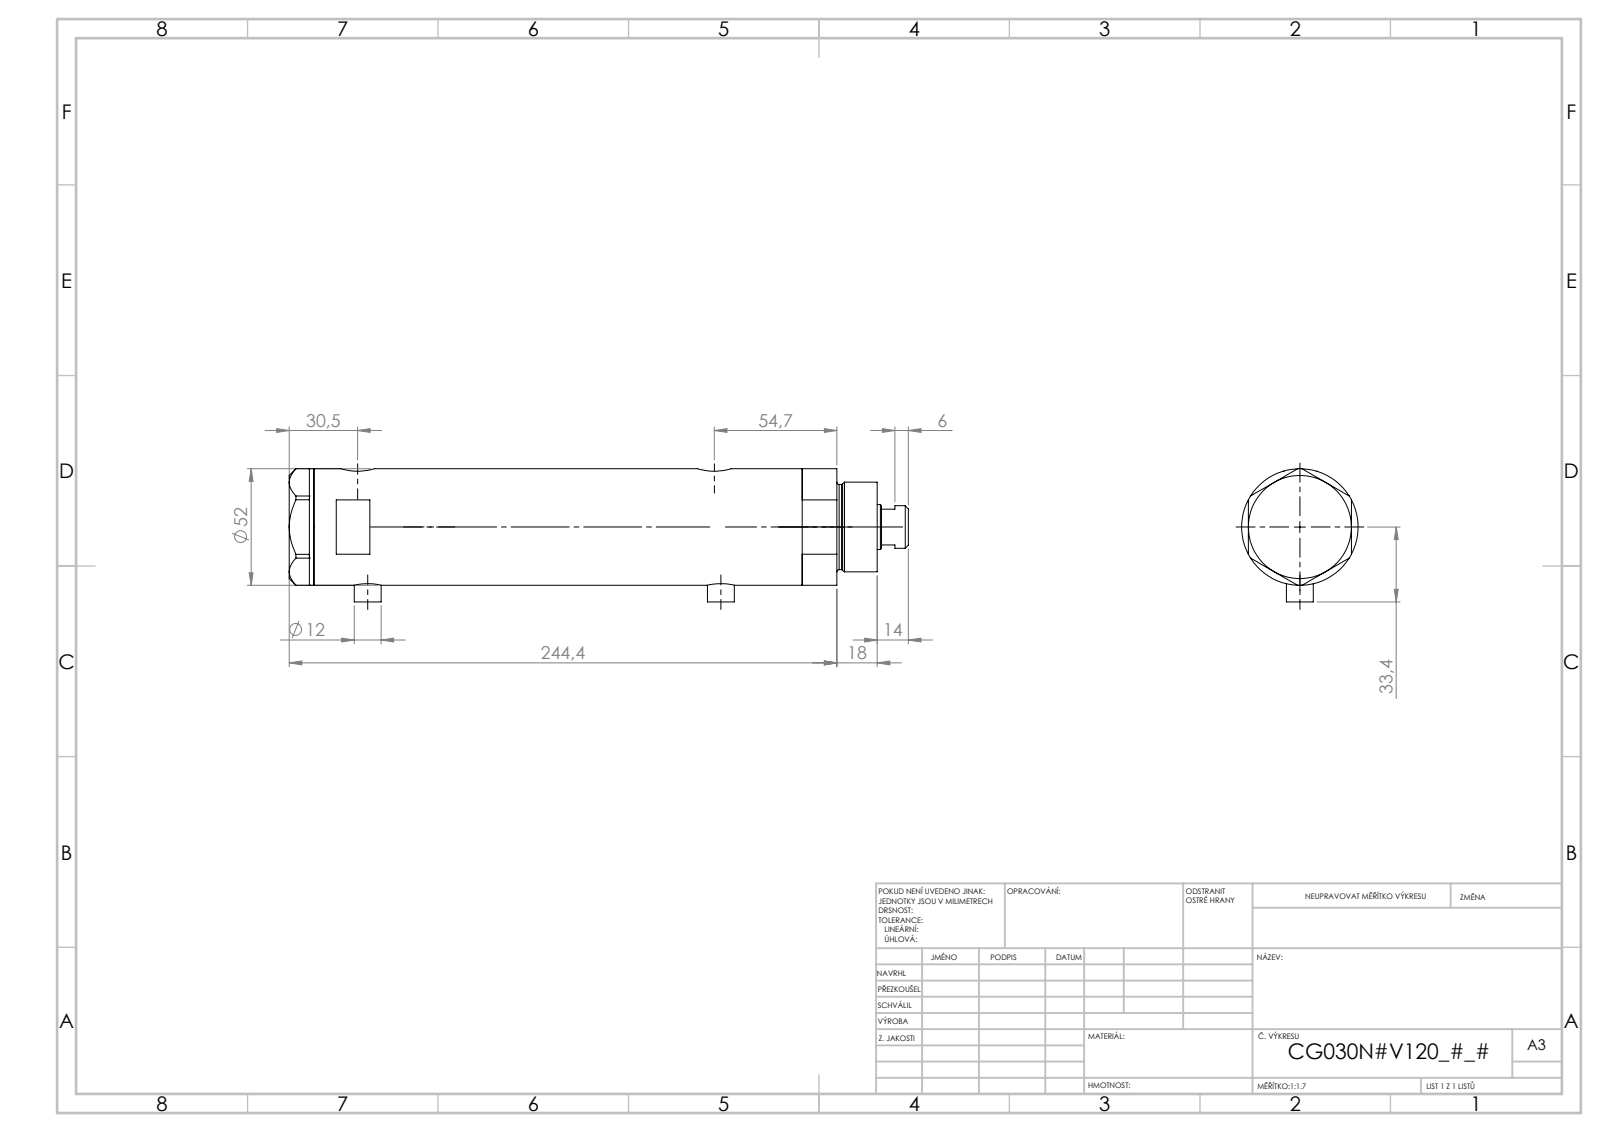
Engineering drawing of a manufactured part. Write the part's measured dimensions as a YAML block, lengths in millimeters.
part_name: "V270CG_FRONT; V270CG_VC; V270CG_MIDDLE; V270CG_BACK"
step_written_by: "SolidWorks 2019 (CONFIG_CONTROL_DESIGN)"
units: millimeters
bodies: {solids: 4, faces: 134, planar: 65, cylindrical: 49, other: 20}
overall_size: [276.3, 59.4, 52]
volume: 492054
surface_area: 106154
round_holes:
  - {diameter: 9.73, count: 2}
  - {diameter: 12.5, count: 2}
  - {diameter: 15, count: 2}
  - {diameter: 6.5, count: 1}
  - {diameter: 20, count: 1}
  - {diameter: 21.5, count: 1}
  - {diameter: 30, count: 1}
  - {diameter: 33, count: 1}
  - {diameter: 44, count: 1}
round_bosses_or_shafts:
  - {diameter: 12, count: 2}
  - {diameter: 52, count: 1}
  - {diameter: 40, count: 1}
  - {diameter: 38, count: 1}
  - {diameter: 19, count: 1}
face_to_face_distances: [181.5, 23.8, 157.7, 11, 34.8, 192.5, 46, 228.9, 217.9, 194.1]
hole_center_spacings: [2.9, 4.5, 154.7, 157.6, 159.2, 162.1]
